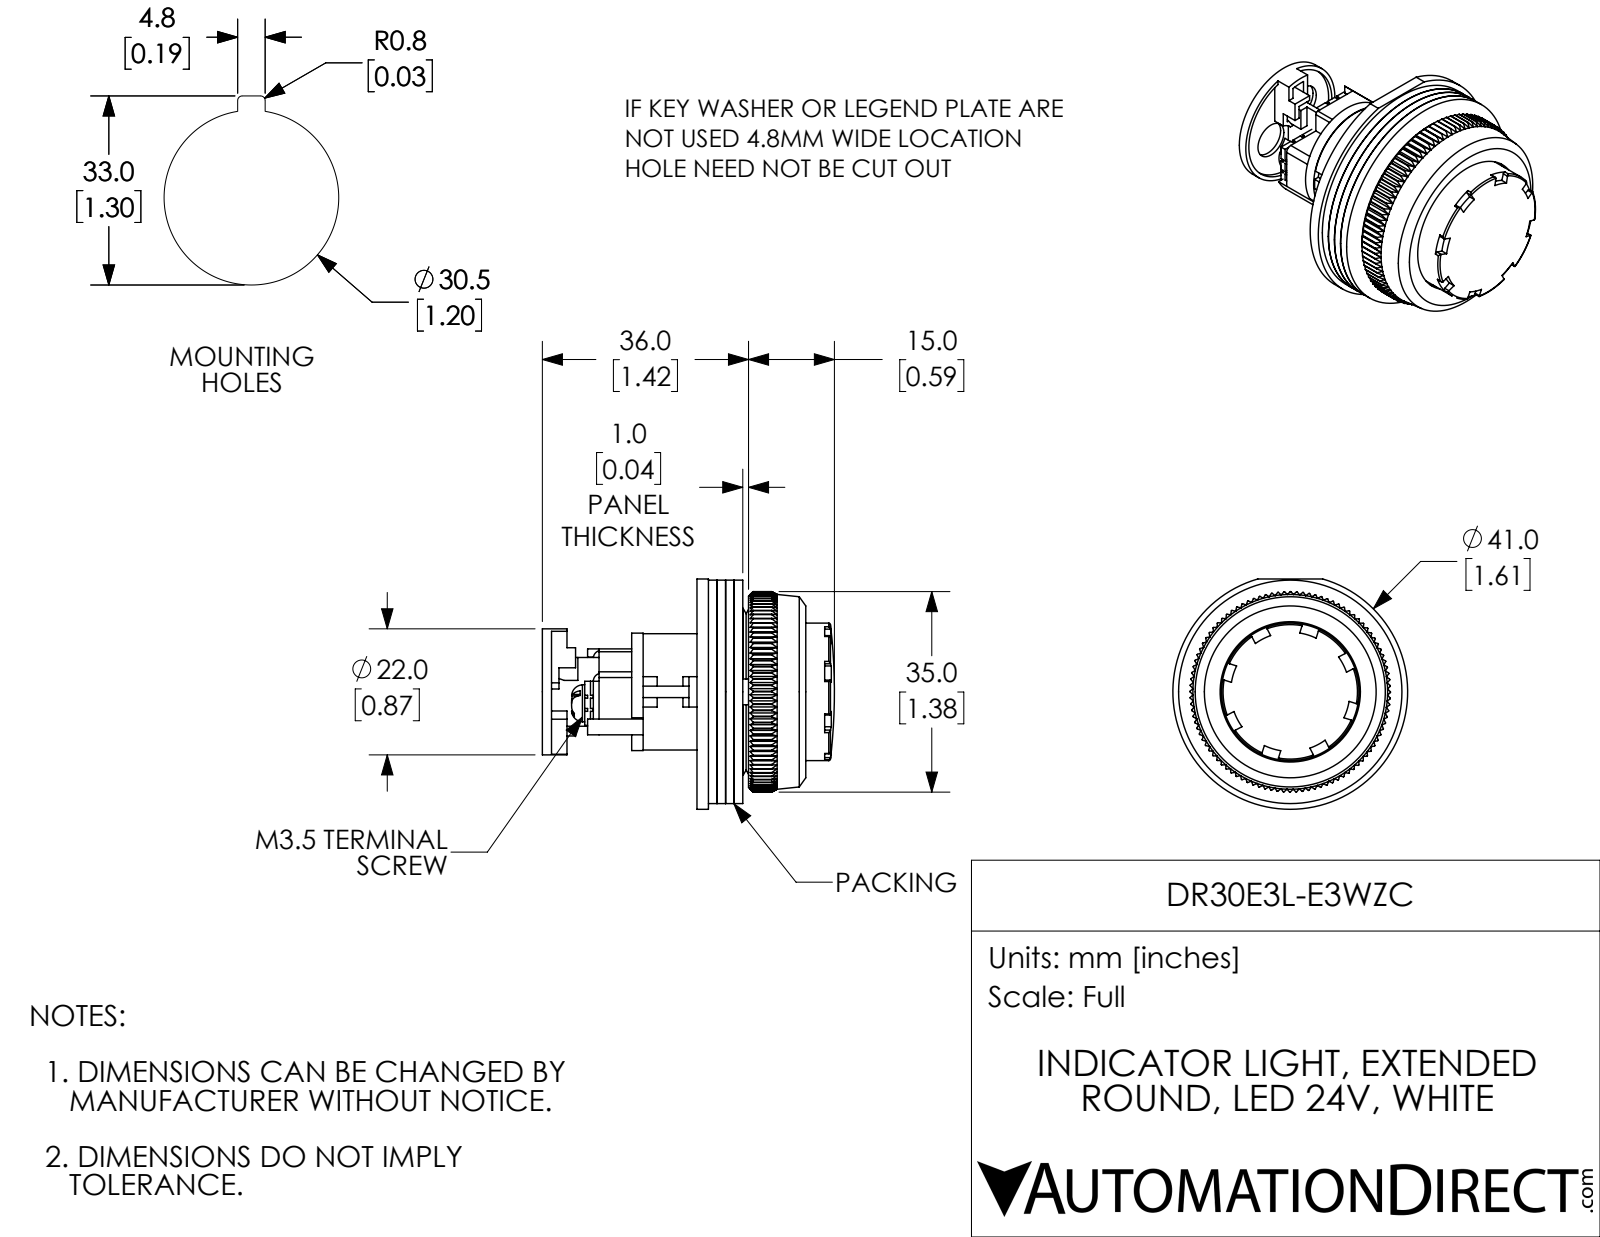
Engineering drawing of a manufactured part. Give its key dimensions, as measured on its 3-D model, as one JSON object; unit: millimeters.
{"part_name": "DR30E3L-E3WZC", "step_written_by": "SolidWorks 2017 (AUTOMOTIVE_DESIGN)", "units": "millimeters", "bodies": {"solids": 16, "faces": 1287, "planar": 717, "cylindrical": 328, "other": 242}, "overall_size": [51, 41, 40.2], "volume_mm3": 17570, "surface_area_mm2": 24230, "round_holes": [[3, 2], [3.5, 2], [6.4, 2], [14.3, 1], [16, 1], [18.3, 1], [20, 1], [20.5, 1], [22, 1], [24.5, 1], [28.5, 1], [29.8, 1]], "round_bosses_or_shafts": [[1.6, 2], [41, 1], [39, 1], [29.5, 1], [24, 1], [21.8, 1], [20.8, 1], [20.3, 1]], "partial_cylinders_radius": [[0.3, 16], [1.5, 8], [0.3, 5], [0.6, 5], [0.4, 4], [1.4, 4], [0.5, 2], [1, 2]], "face_to_face_distances": [1.5, 3, 4.5, 1, 5, 2, 8, 6.5, 2.5, 6], "hole_center_spacings": [4.5, 4.7, 9.2, 8.9, 9.4]}
